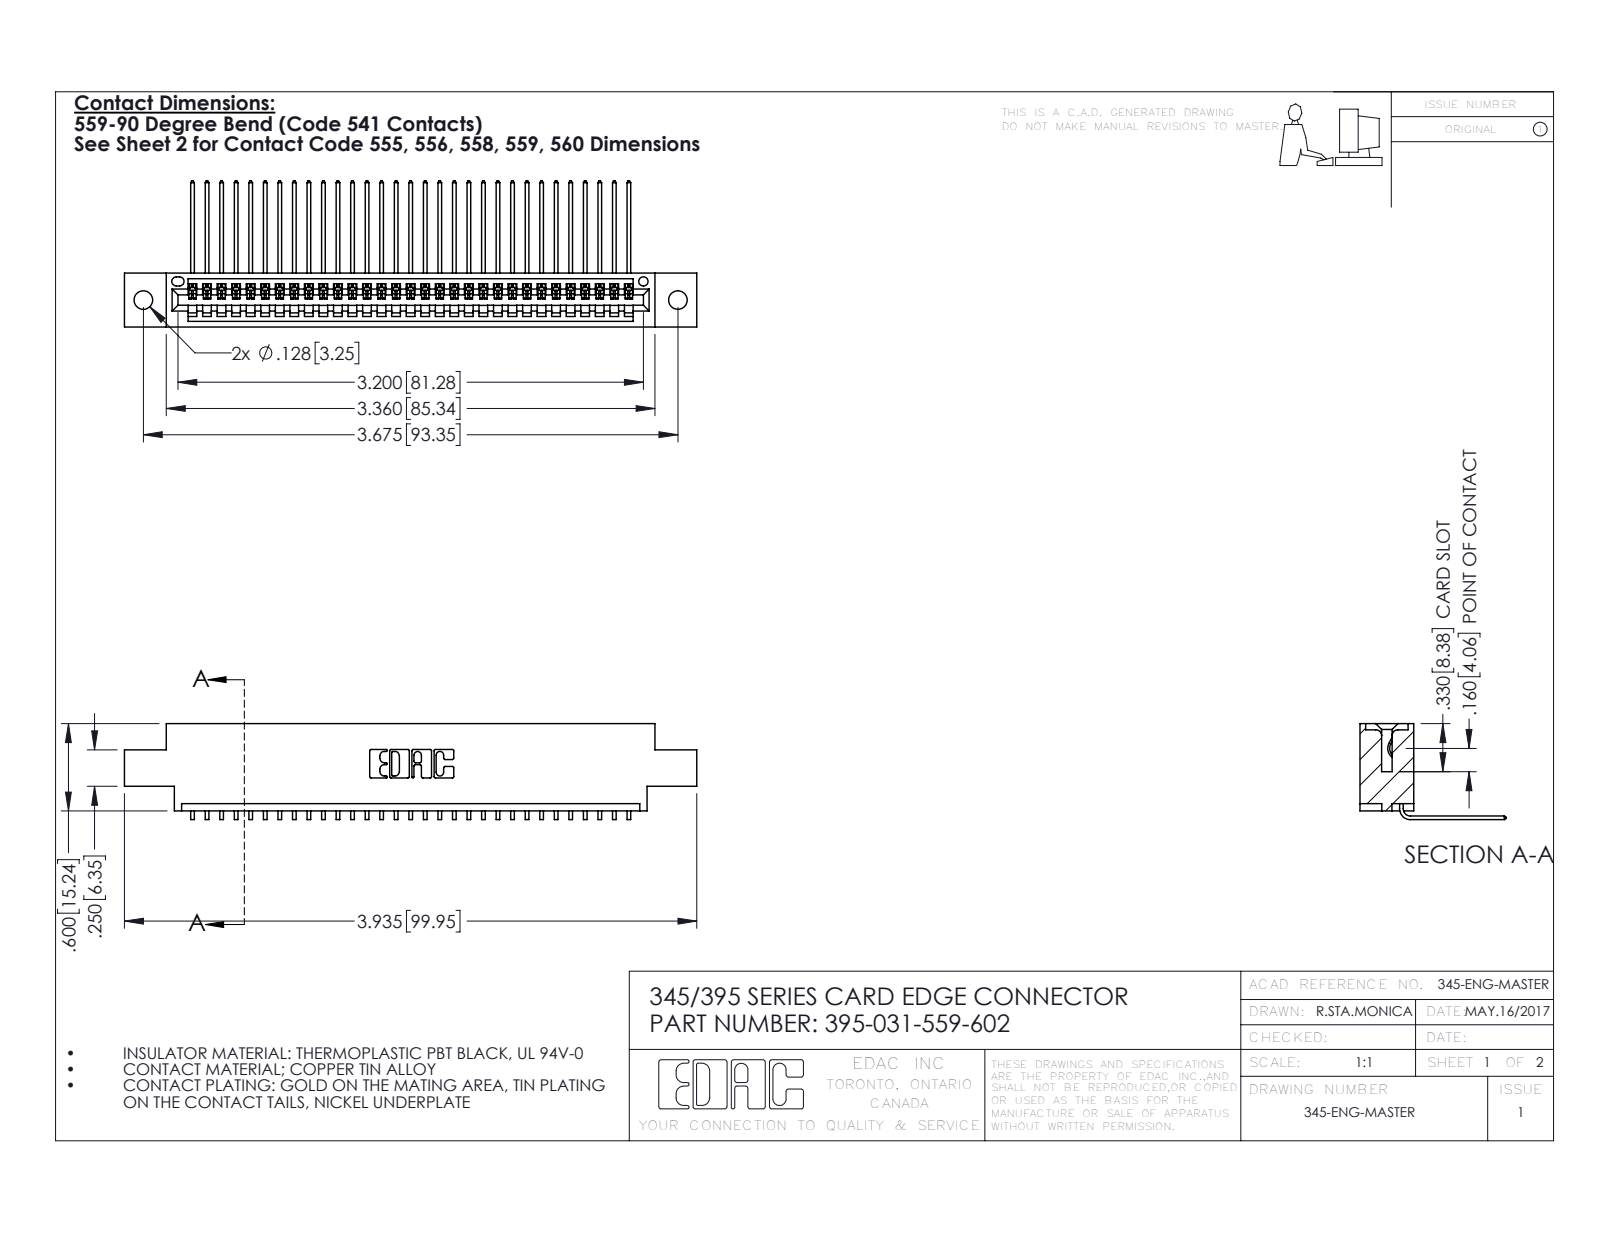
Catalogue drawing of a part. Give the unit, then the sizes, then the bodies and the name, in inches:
Units: inches
Overall size (bounding box): 3.935 × 1.005 × 0.659
Round holes (diameter × count): ⌀0.128 ×2, ⌀0.064 ×1
Partial cylindrical surfaces — rounded edges, fillets, slot ends (radius × count): R0.006 ×62, R0.01 ×22, R0.007 ×6, R0.031 ×6, R0.026 ×3, R0.031 ×2, R0.04 ×2, R0.014 ×1
Main face-to-face distances: 0.072, 0.298, 0.37, 0.2, 0.098, 0.272, 0.025, 0.225, 0.175, 0.149
Hole centre spacings: 0.27, 3.44, 3.675
Volume: 0.571 in³ · Surface area: 19.76 in²
Bodies: 32 solids, 1990 faces (1386 planar, 604 cylindrical, 0 other)
Part name (STEP PRODUCT): 395-031-559-602; 345 Part_0.170 Offset - 0.128 Dia; 345-292-001_558 559 Tail - 1
STEP written by: SolidWorks 2016 (CONFIG_CONTROL_DESIGN)
